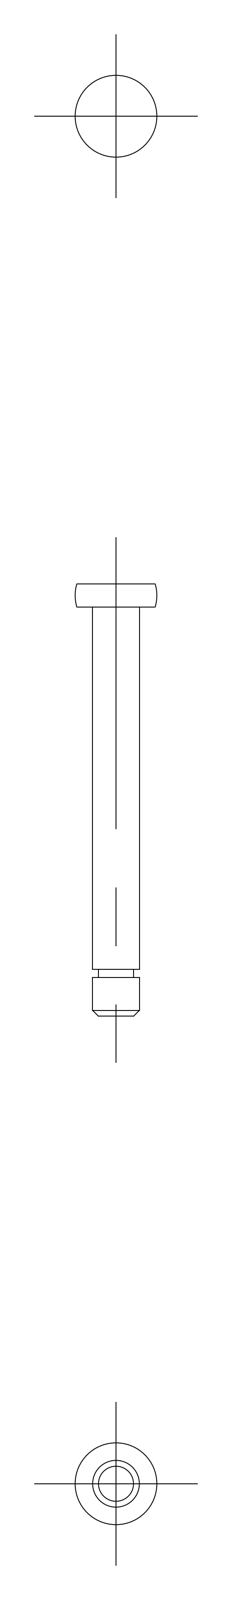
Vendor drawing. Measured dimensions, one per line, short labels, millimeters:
name: shaft
written by: CADfix (AUTOMOTIVE_DESIGN)
unit: mm
bodies: 1 solid, 14 faces (0 planar, 0 cylindrical, 14 other)
size: 37 × 7 × 7
volume: 510 mm³; area: 560 mm²
